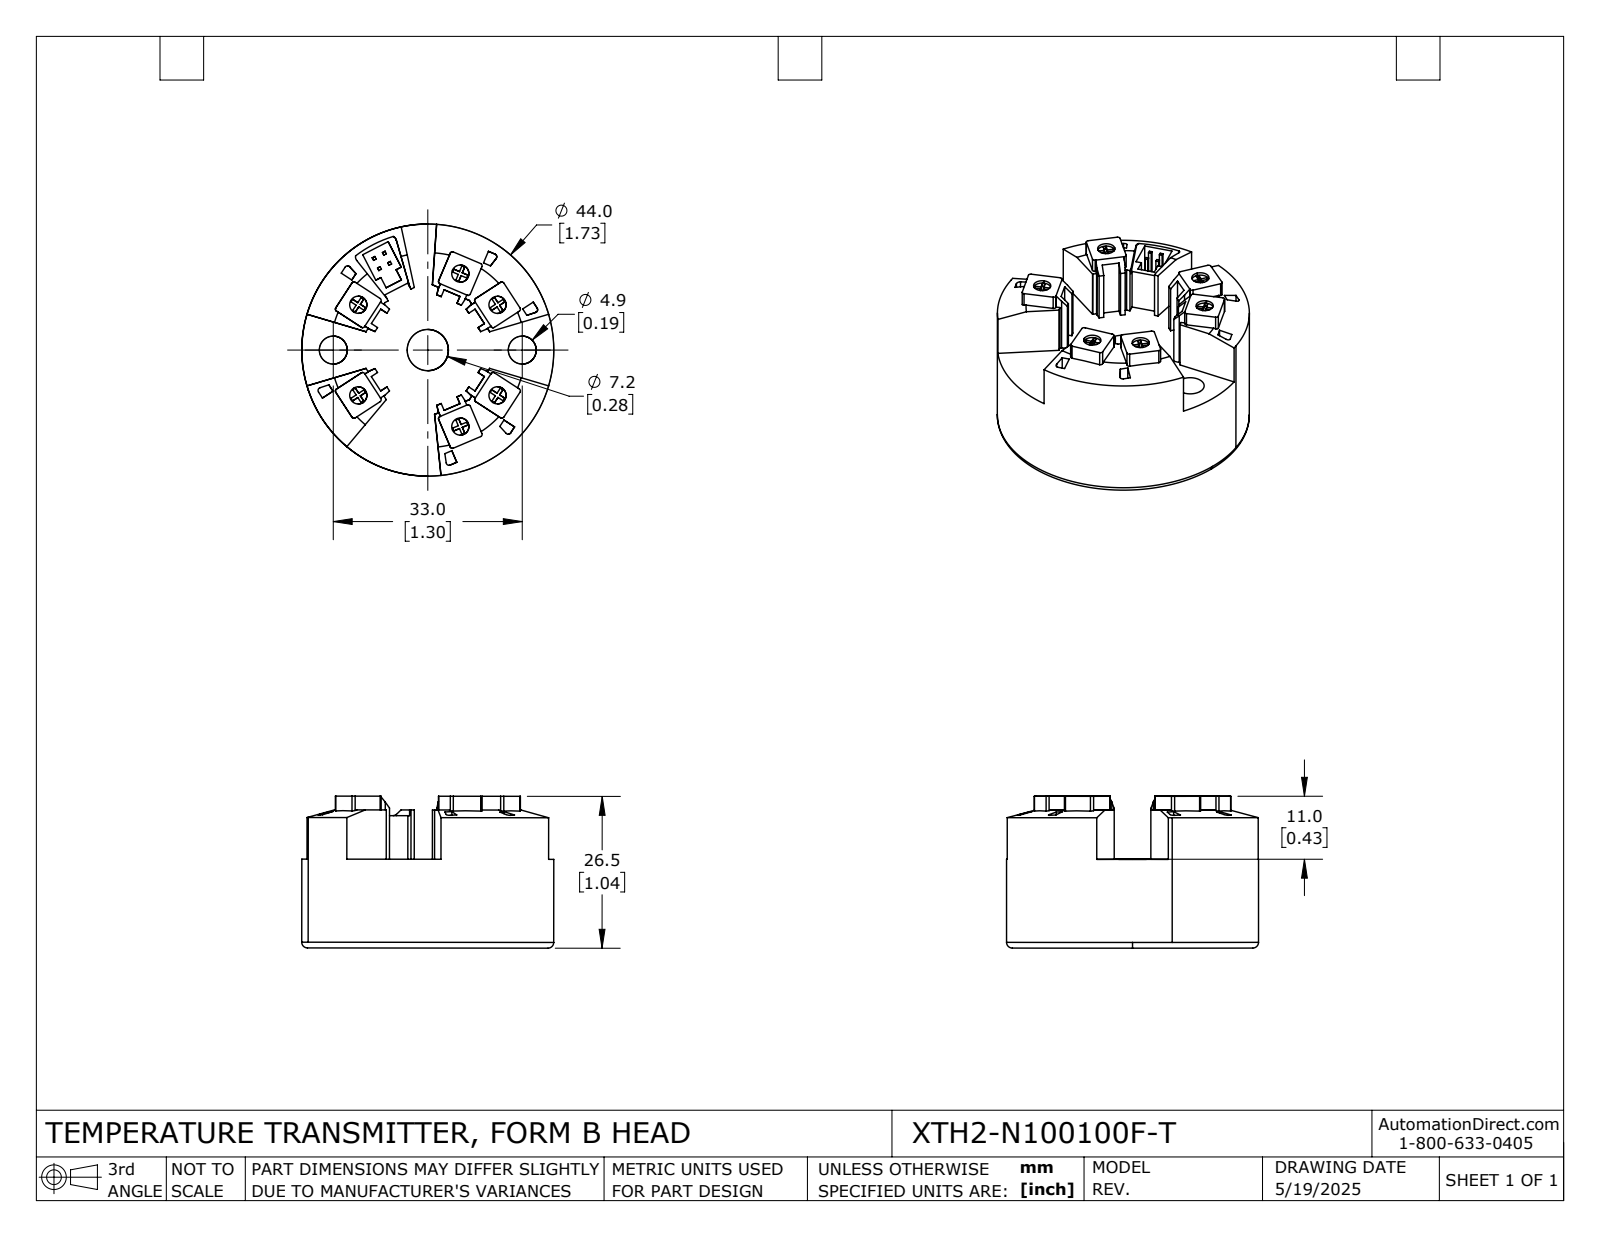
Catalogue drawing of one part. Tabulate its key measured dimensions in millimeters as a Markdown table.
| quantity | value |
| --- | --- |
| part name | XTDH2-N100100F-T |
| STEP written by | SolidWorks 2024 (AUTOMOTIVE_DESIGN) |
| units | millimeters |
| bodies | 1 solid, 341 faces (281 planar, 52 cylindrical, 8 other) |
| overall size | 44 × 44 × 26.5 |
| volume | 28 640 mm³ |
| surface area | 8 684 mm² |
| round holes (diameter × count) | 3 × 6, 4.9 × 2, 7.2 × 1 |
| round bosses / shafts (diameter × count) | 44 × 1 |
| partial cylindrical surfaces (radius × count) | 0.4 × 24, 0.5 × 6, 1 × 2 |
| main face-to-face distances | 15.5, 26.5, 11, 1.5, 4.5, 1, 0.5, 3, 24.1, 8.6 |
| hole center spacings | 14.5, 8.5, 9, 9, 16.5, 17.2, 18.6, 22.2 |
